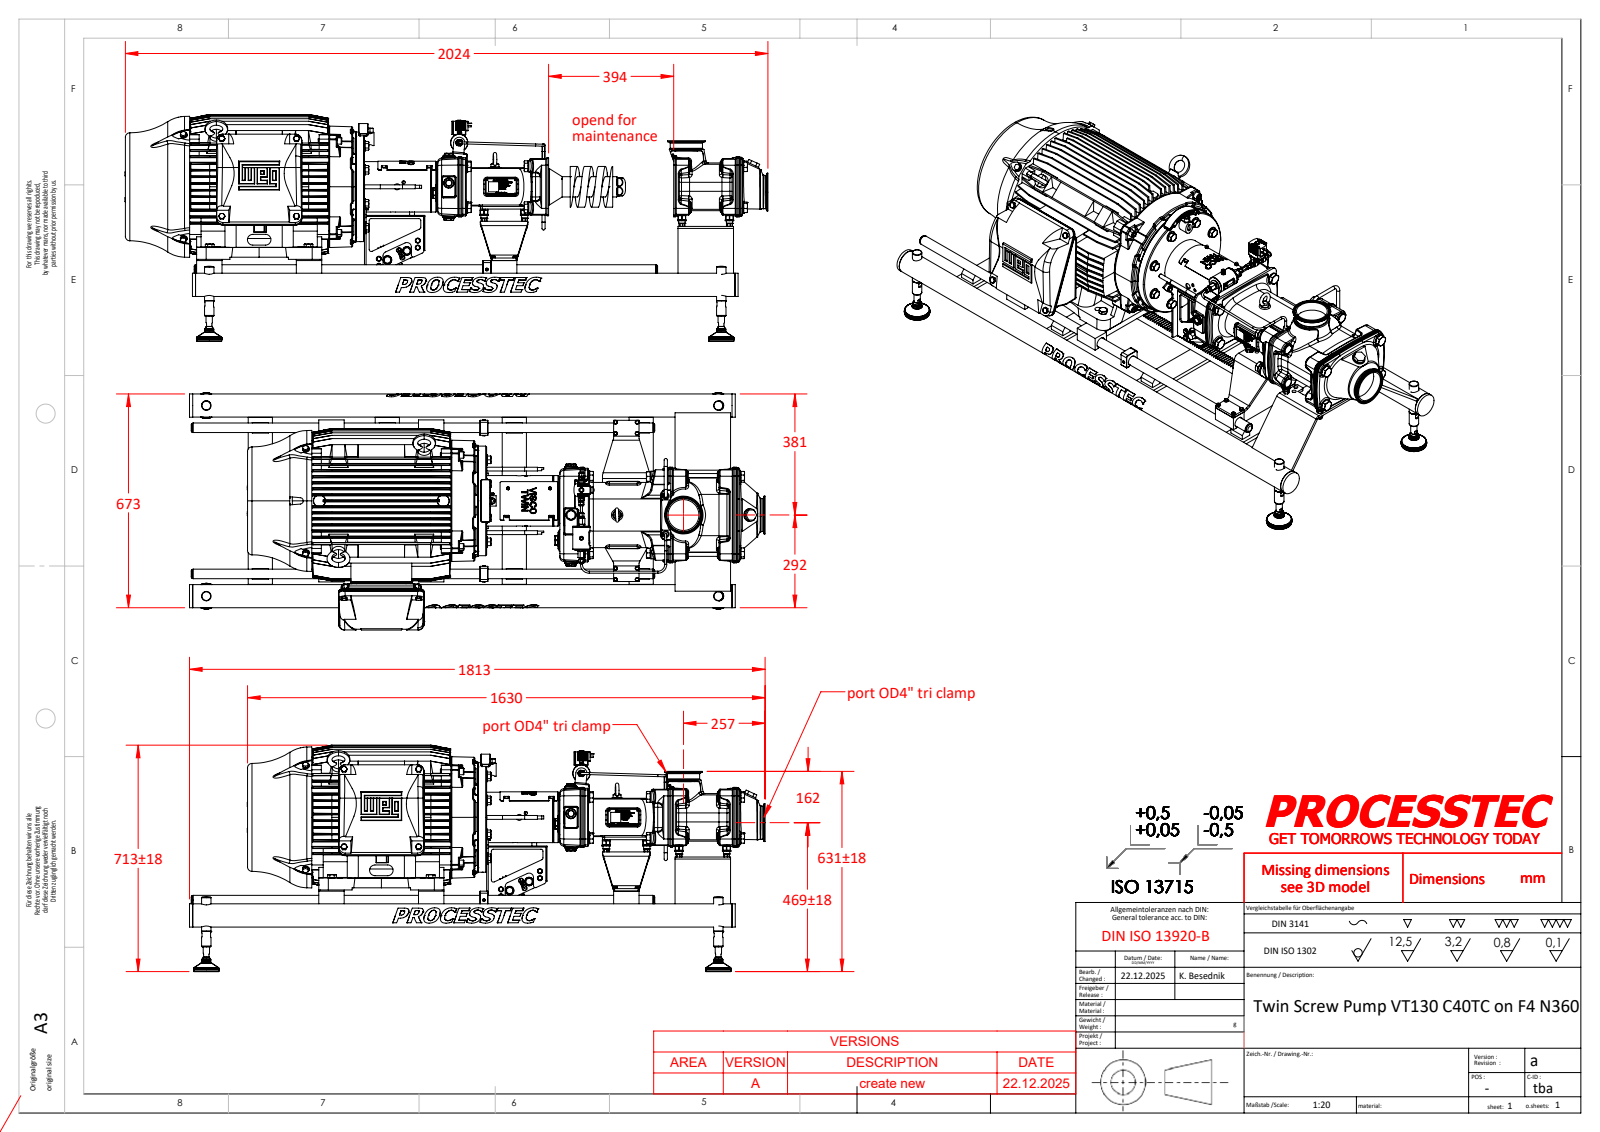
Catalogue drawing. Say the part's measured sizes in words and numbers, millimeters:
The part is named "Flat Washer Type A Narrow 5-8 0p625_Preferred Narrow FW 0.625; 001082; 001104_ISO 10642 - M6 x 16 - 16N; 000955 (+8 more)". Its 3-D file was written by "SolidWorks 2023 (AUTOMOTIVE_DESIGN)". It is 249 solids with 19713 faces: 7786 planar, 3453 cylindrical and 8474 other. Overall it measures 1813 by 747.06 by 713.13 millimeters. Its volume is 142 600 000 cubic millimeters and its surface area 10 110 000 square millimeters. Round holes: 24 of diameter 8.5, 22 of diameter 5, 22 of diameter 6.8, 13 of diameter 13, 13 of diameter 17.5, 11 of diameter 4.1, 10 of diameter 15.87, 9 of diameter 10.5, 9 of diameter 25, 8 of diameter 6.4, 8 of diameter 10.1, 8 of diameter 10.25. Round bosses or shafts: 40 of diameter 10, 21 of diameter 6, 16 of diameter 24, 16 of diameter 20, 15 of diameter 16, 14 of diameter 8, 11 of diameter 17, 11 of diameter 12. Partial cylindrical surfaces (rounded edges, fillets, slot ends): 89 of radius 1.5, 80 of radius 3, 65 of radius 18, 51 of radius 2, 45 of radius 6, 41 of radius 4, 33 of radius 3.2, 31 of radius 6.35. The main face-to-face distances are 438, 8, 12.7, 19.06, 189.44, 18.8, 851.65, 413.65, 150.89, 37.58. The hole center spacings are 461.41, 400, 129.3, 230, 832.41, 55, 11, 139.7.
